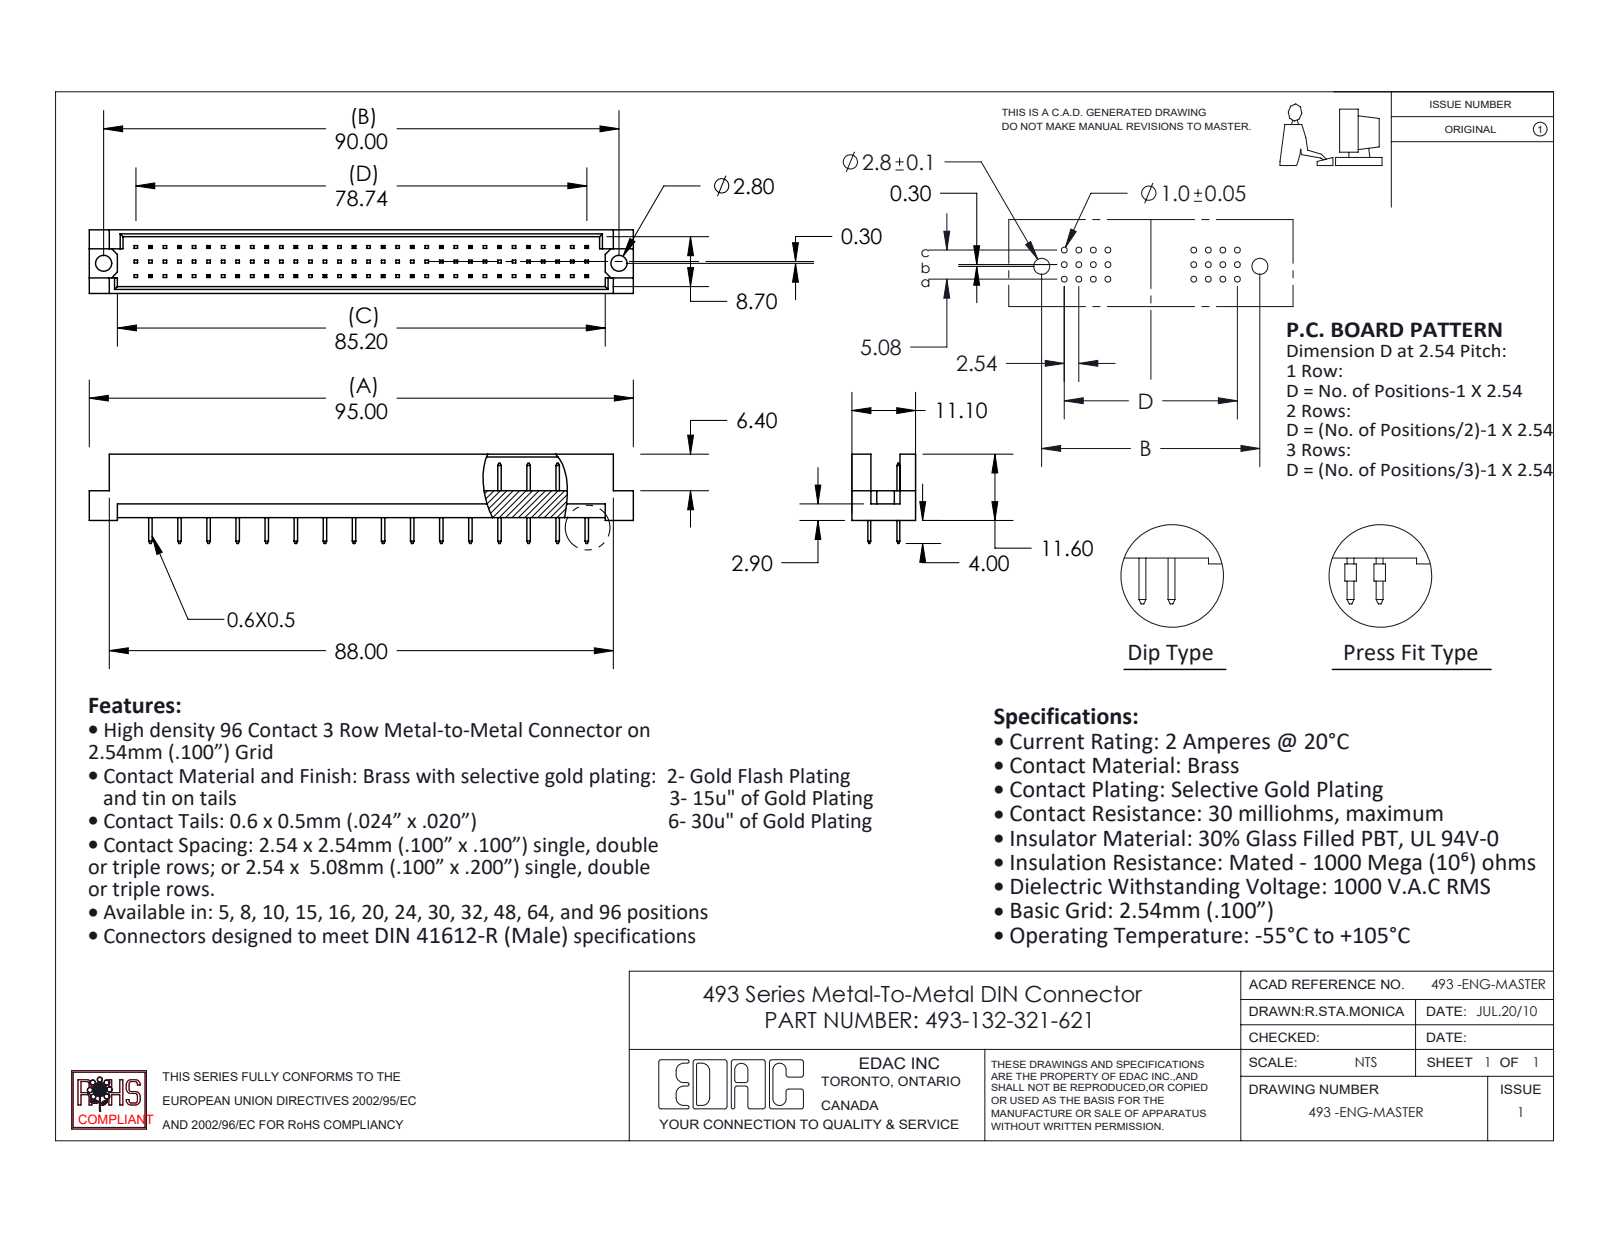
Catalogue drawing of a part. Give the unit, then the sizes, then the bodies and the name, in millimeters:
Units: millimetres
Overall size (bounding box): 95 × 15.6 × 11.1
Round holes (diameter × count): ⌀2.8 ×2
Main face-to-face distances: 1.2, 9.9, 11.1, 8.7, 5.08, 4.7, 0.5, 2.76, 3.26, 7.84
Hole centre spacings: 90
Volume: 5 790 mm³ · Surface area: 7 448 mm²
Bodies: 33 solids, 884 faces (880 planar, 4 cylindrical, 0 other)
Part name (STEP PRODUCT): 493-290_21; 493-132-321-621; 493 Part_96
STEP written by: SolidWorks 2020 (CONFIG_CONTROL_DESIGN)
